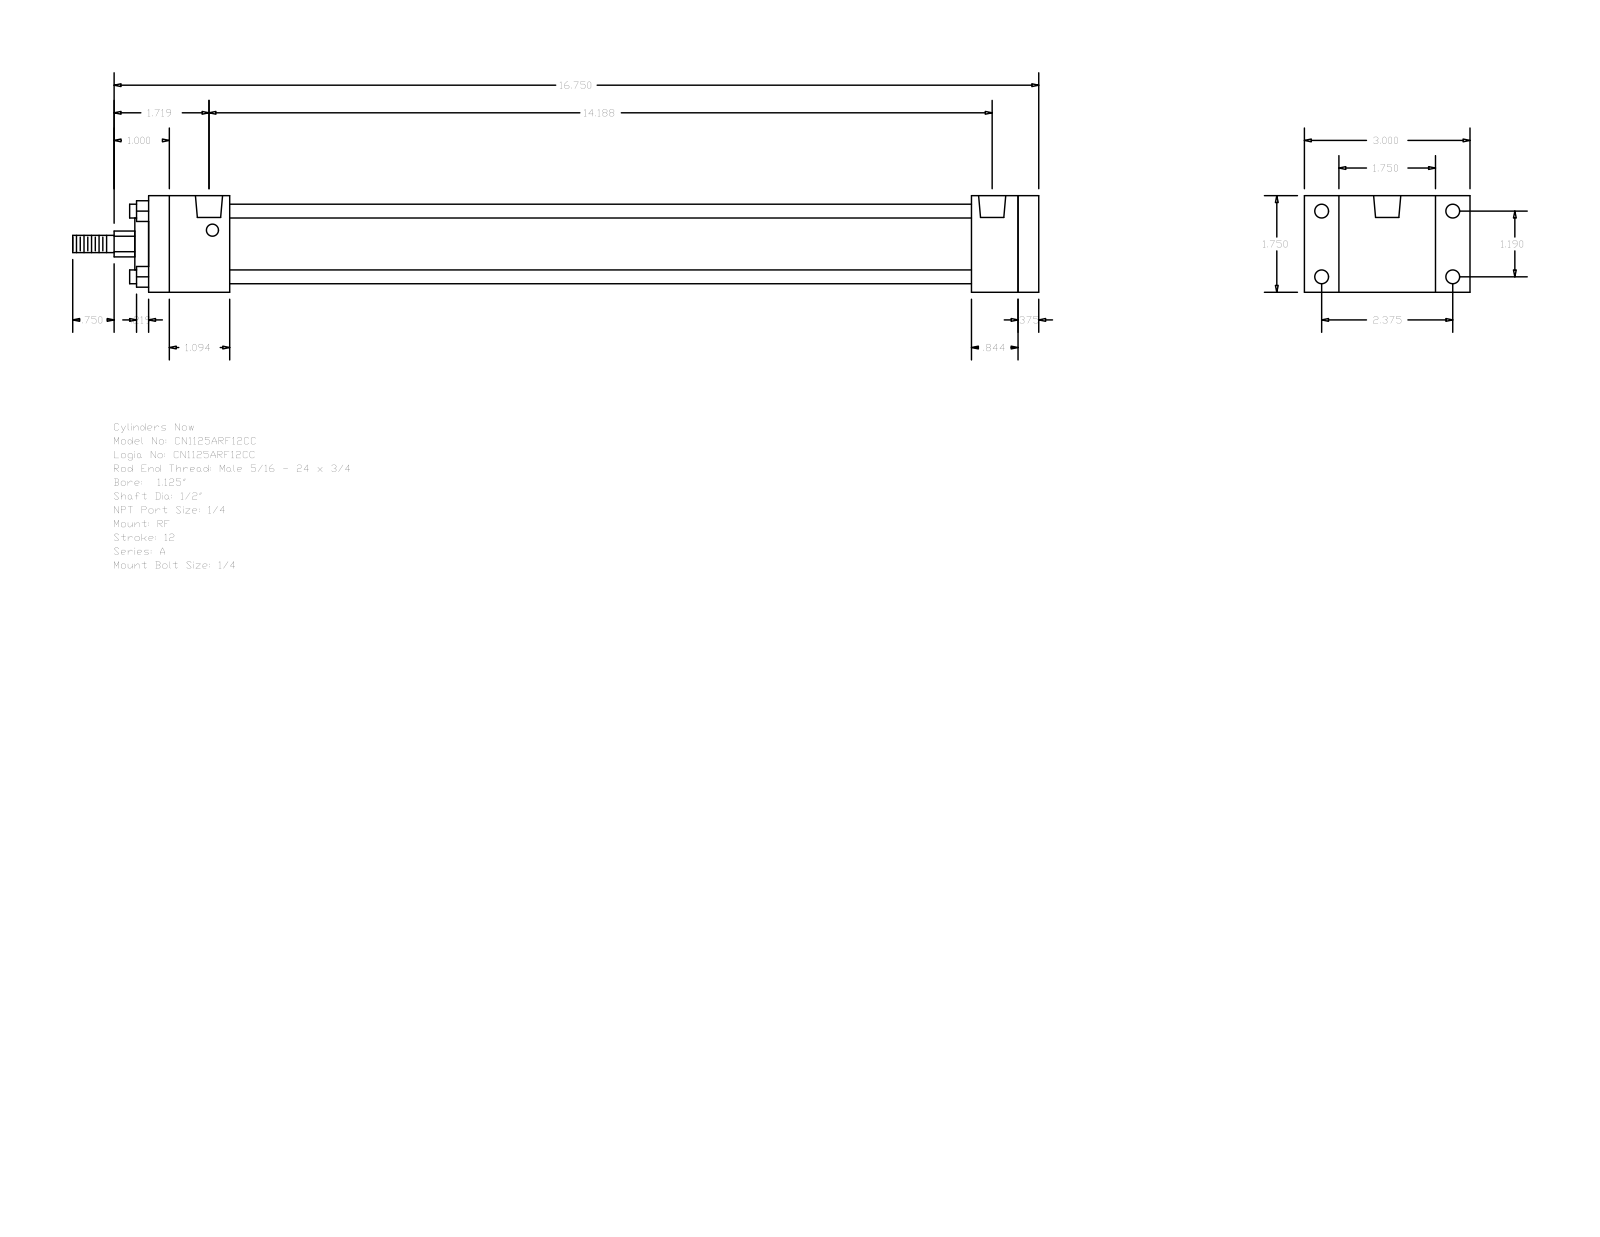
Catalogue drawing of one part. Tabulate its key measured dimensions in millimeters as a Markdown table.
| quantity | value |
| --- | --- |
| part name | A_RF__0112_0.5 |
| STEP written by | GSSL Pune (CONFIG_CONTROL_DESIGN) |
| units | millimeters |
| bodies | 0 solids, 92 faces (64 planar, 28 cylindrical, 0 other) |
| overall size | 444.5 × 76.2 × 44.45 |
| round holes (diameter × count) | 5.56 × 4, 6.35 × 4, 12.49 × 2 |
| round bosses / shafts (diameter × count) | 6.35 × 4, 31.88 × 1, 23.81 × 1, 12.7 × 1, 7.94 × 1 |
| partial cylindrical surfaces (radius × count) | 5.94 × 1 |
| main face-to-face distances | 44.46, 9.52, 400.05, 409.57, 37.3, 378.61, 341.31, 362.75, 372.27, 21.44 |
| hole center spacings | 30.22, 60.32, 67.47, 357.19, 1.58, 1.59, 358.77, 358.78 |
